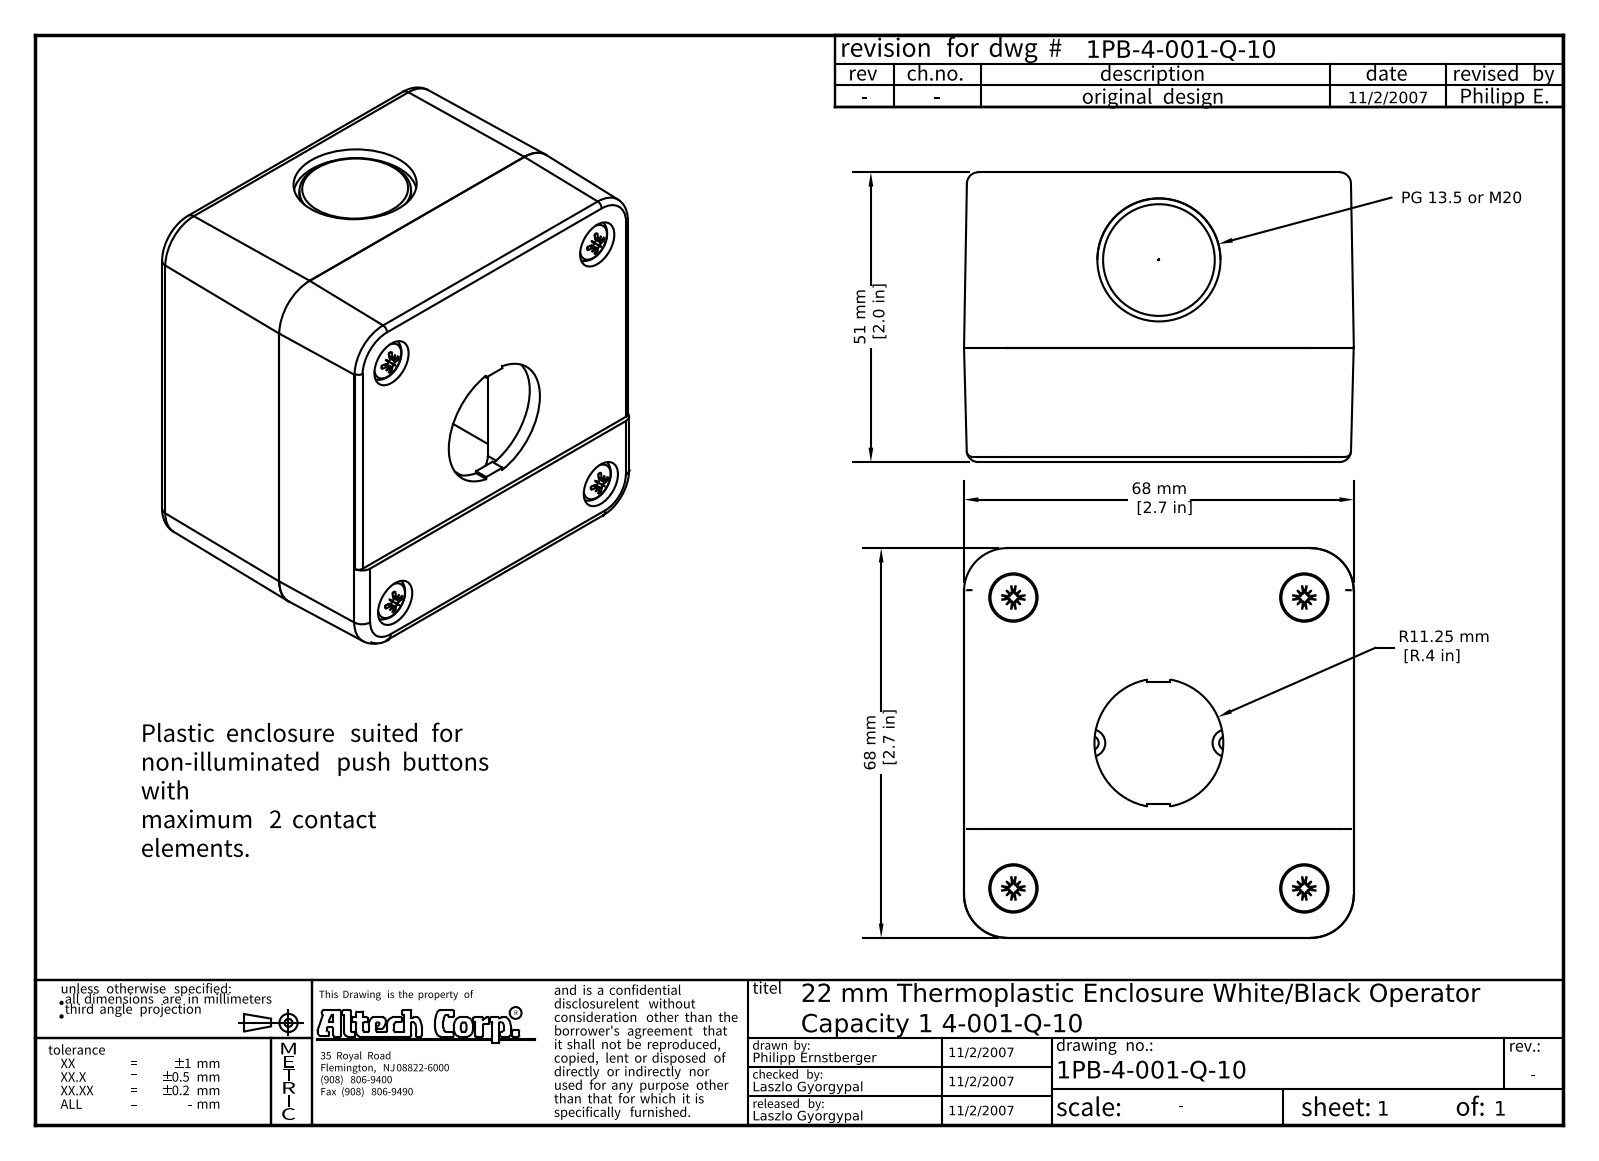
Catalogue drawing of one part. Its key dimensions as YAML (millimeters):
part_name: "4-001-Q-10; Teknic_enclousure_back; Teknic_enclousure; NF EN ISO 7045 - Z M4 x 30 - 4.8 - Z"
step_written_by: "Autodesk Inventor 2008 (AUTOMOTIVE_DESIGN)"
units: millimeters
bodies: {solids: 6, faces: 448, planar: 199, cylindrical: 79, other: 170}
overall_size: [68.07, 68.07, 50.6]
volume: 53482
surface_area: 71125
round_holes:
  - {diameter: 1.5, count: 2}
  - {diameter: 4.45, count: 2}
  - {diameter: 8.45, count: 2}
  - {diameter: 21.5, count: 2}
  - {diameter: 2.5, count: 1}
  - {diameter: 22.5, count: 1}
round_bosses_or_shafts:
  - {diameter: 4, count: 4}
  - {diameter: 3.62, count: 4}
  - {diameter: 19.5, count: 2}
  - {diameter: 9.45, count: 2}
  - {diameter: 5.45, count: 2}
  - {diameter: 23.5, count: 1}
  - {diameter: 4.81, count: 1}
  - {diameter: 3.36, count: 1}
partial_cylinders:
  - {radius: 2, count: 7}
  - {radius: 3, count: 4}
  - {radius: 3.5, count: 4}
  - {radius: 4, count: 4}
  - {radius: 5, count: 4}
  - {radius: 6.5, count: 4}
  - {radius: 7, count: 4}
  - {radius: 7.3, count: 4}
face_to_face_distances: [0.5, 2, 3.1, 49.2, 46.6, 49.7, 46.1, 0.9, 43.25, 1.5]
hole_center_spacings: [6.67, 35.92, 11.76, 13, 14.76, 14.77, 22.47, 28.84]
